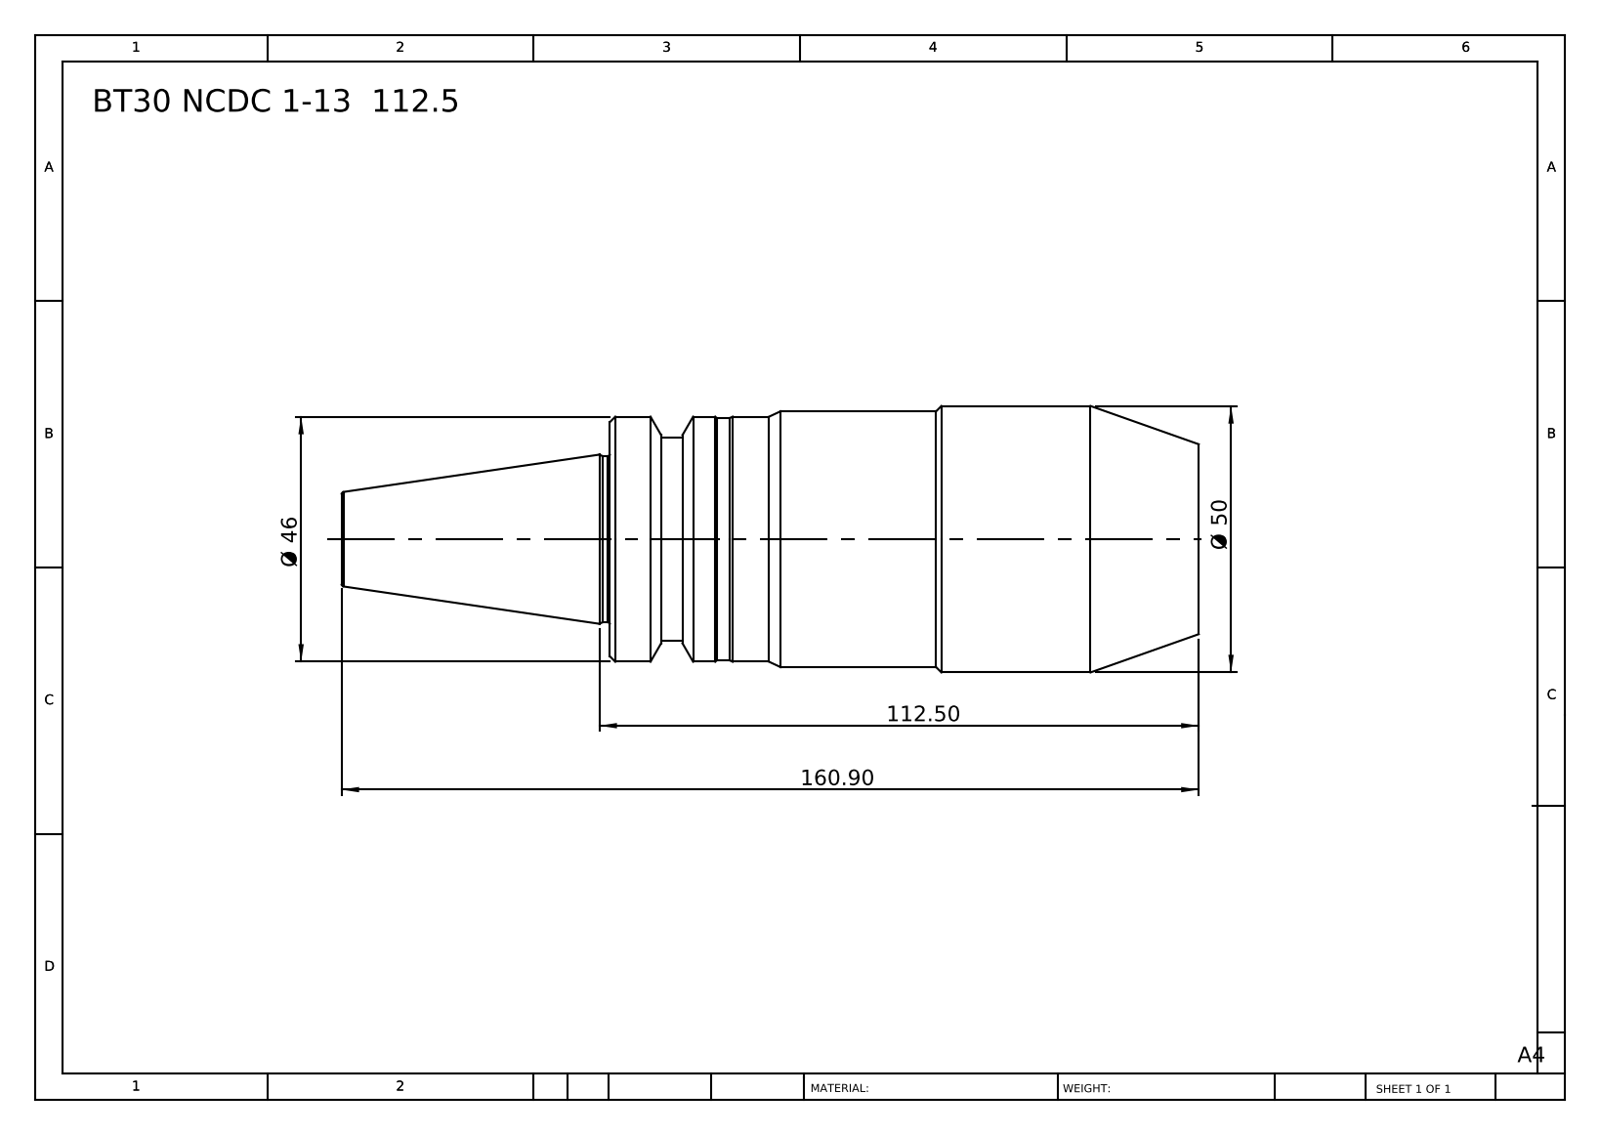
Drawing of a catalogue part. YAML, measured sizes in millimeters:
part_name: "BT30 NCDC 1-13 112.5"
step_written_by: "SolidWorks 2014 (CONFIG_CONTROL_DESIGN)"
units: millimeters
bodies: {solids: 1, faces: 45, planar: 5, cylindrical: 16, other: 24}
overall_size: [160.9, 50, 50]
volume: 214660
surface_area: 23143
round_bosses_or_shafts:
  - {diameter: 50, count: 1}
  - {diameter: 48, count: 1}
  - {diameter: 46, count: 1}
  - {diameter: 45.5, count: 1}
  - {diameter: 38, count: 1}
  - {diameter: 31.2, count: 1}
face_to_face_distances: [110.5, 160.9, 50.4, 100.9, 9.6, 60, 96.9, 4, 13.6, 64]
